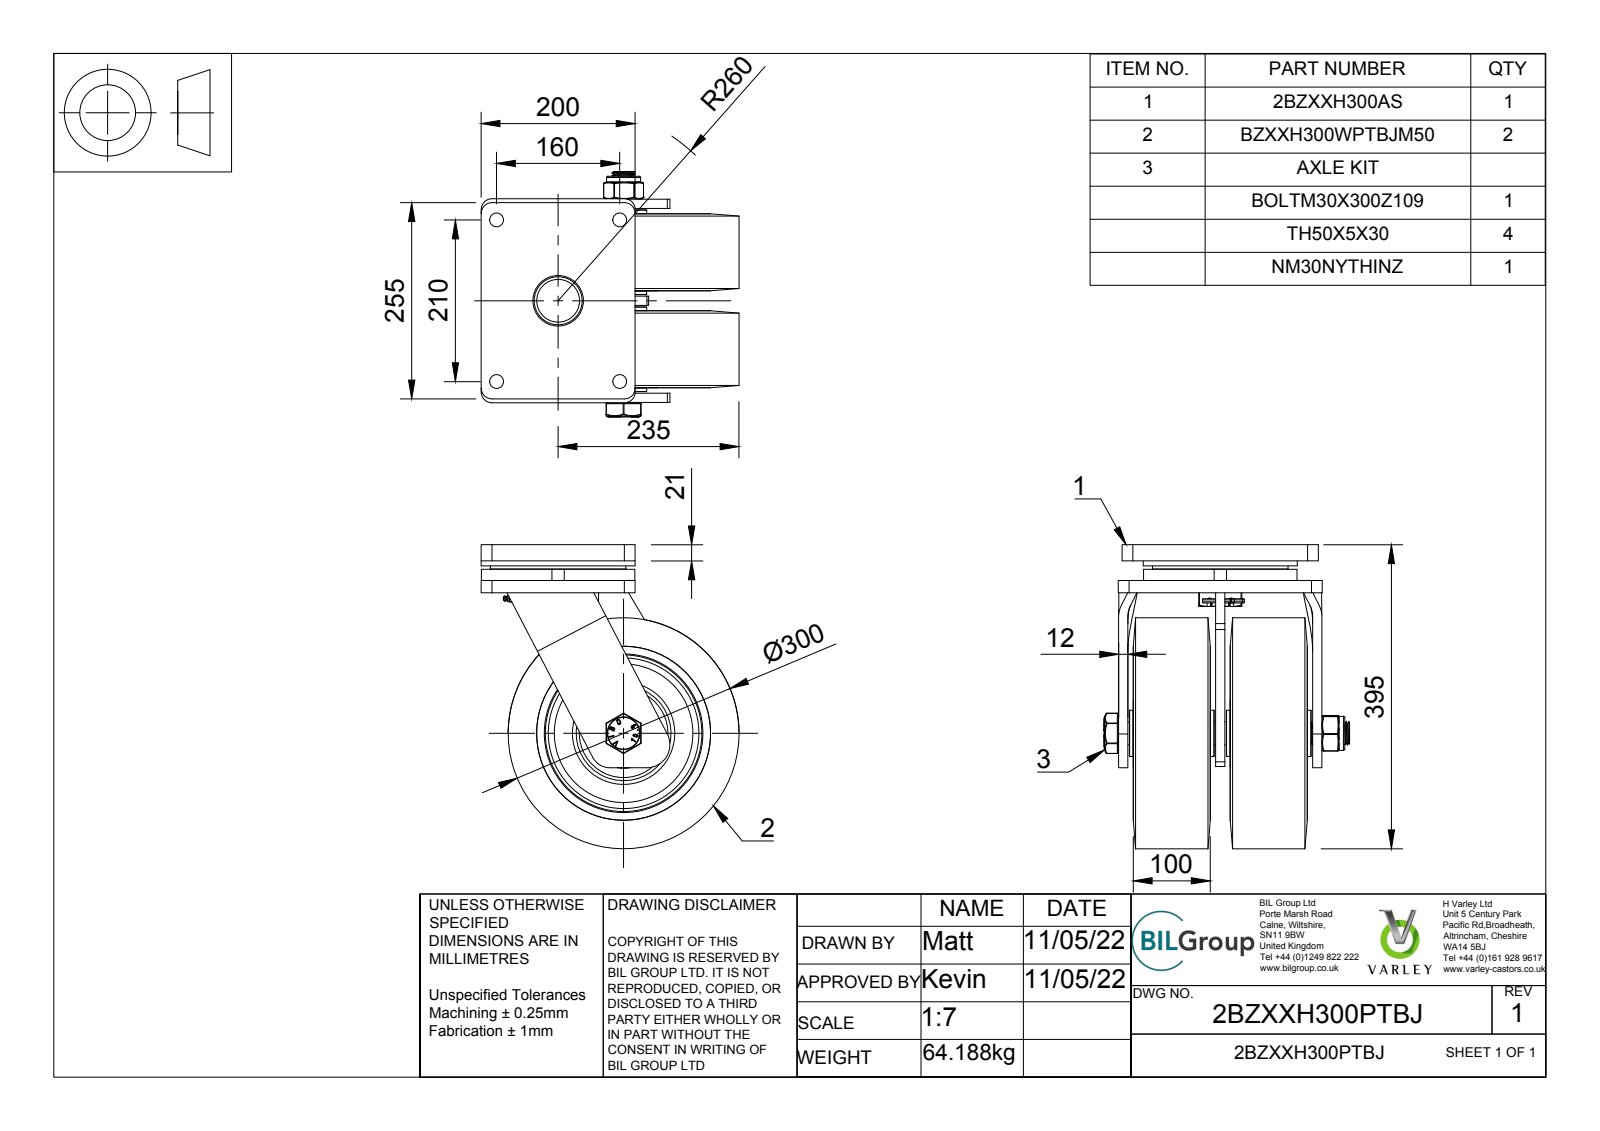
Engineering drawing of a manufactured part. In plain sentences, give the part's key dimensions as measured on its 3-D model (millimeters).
The part is named "2BZXXH300PTBJ v4; 2BZXXH300PTBJ v1 (1); 2BZXXH300AS; FABRICATED STEEL TOP PLATE (+8 more)". Its 3-D file was written by "Autodesk Translation Framework v13.20.0.188 (AP242_MANAGED_MODEL_BASED_3D_ENGINEERING_MIM_LF)". It is 78 solids with 2275 faces: 729 planar, 398 cylindrical and 1148 other. Overall it measures 395 by 335.01 by 319 millimeters. Its volume is 14 030 000 cubic millimeters and its surface area 1 697 000 square millimeters. Round holes: 4 of diameter 18, 2 of diameter 50, 2 of diameter 62.51, 2 of diameter 63.61, 2 of diameter 64.8, 2 of diameter 79.11, 2 of diameter 81.61, 2 of diameter 84.06, 1 of diameter 5, 1 of diameter 7.25, 1 of diameter 30, 1 of diameter 30.2. Round bosses or shafts: 2 of diameter 90, 2 of diameter 80.11, 2 of diameter 64.61, 2 of diameter 60.06, 1 of diameter 300, 1 of diameter 200, 1 of diameter 176, 1 of diameter 60. Partial cylindrical surfaces (rounded edges, fillets, slot ends): 22 of radius 2, 18 of radius 1, 14 of radius 1.5, 8 of radius 0.34, 8 of radius 0.34, 8 of radius 0.34, 8 of radius 0.35, 8 of radius 0.97. The main face-to-face distances are 126, 12, 21, 41.5, 62.5, 126.01, 40, 252, 60, 20. The hole center spacings are 132, 160, 210, 264.01, 33.51, 101.92, 131.99, 140.26.
